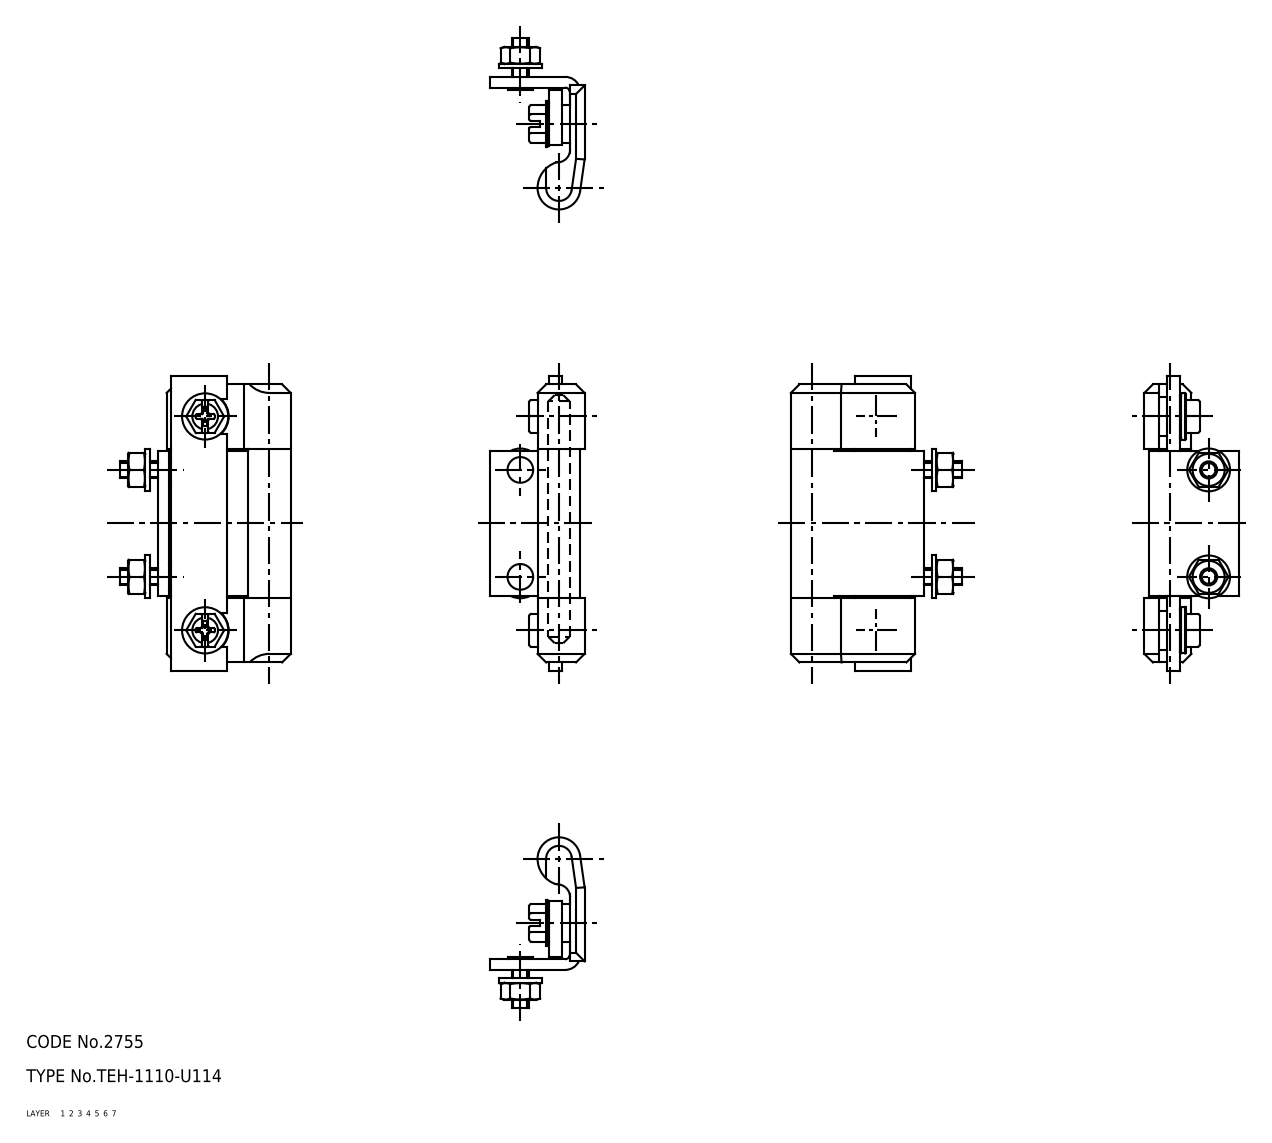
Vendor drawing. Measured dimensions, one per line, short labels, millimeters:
name: hinge pieces_B_mr; screw; nut; washer (+5 more)
written by: CADfix (AUTOMOTIVE_DESIGN)
unit: mm
bodies: 11 solids, 346 faces (0 planar, 0 cylindrical, 346 other)
size: 69 × 40 × 22.02
volume: 14 246 mm³; area: 13 084 mm²
